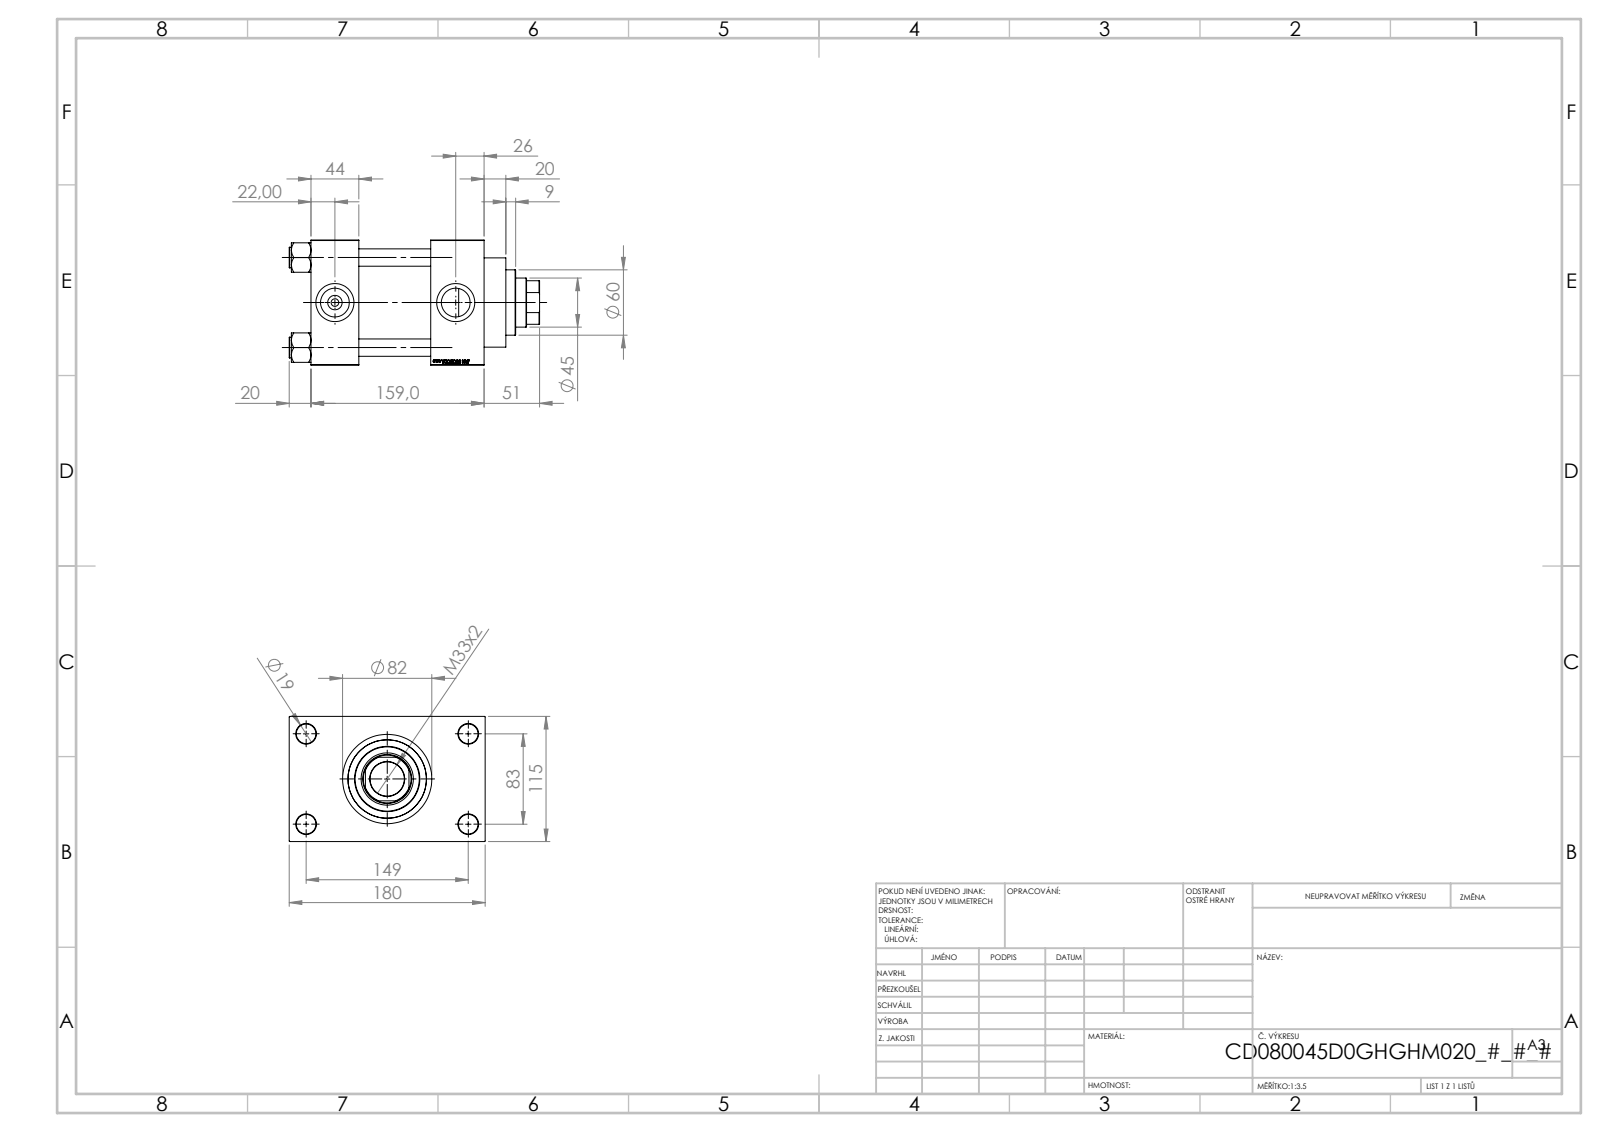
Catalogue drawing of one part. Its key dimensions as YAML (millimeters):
part_name: "V215CD_D_Body; V215CD_VCP_D; V215CD_VC_A; V215CD_NUT_M5_D (+1 more)"
step_written_by: "SolidWorks 2019 (CONFIG_CONTROL_DESIGN)"
units: millimeters
bodies: {solids: 11, faces: 1151, planar: 545, cylindrical: 88, other: 518}
overall_size: [230, 180, 115]
volume: 2004000
surface_area: 302449
round_holes:
  - {diameter: 16, count: 4}
  - {diameter: 18, count: 4}
  - {diameter: 7, count: 2}
  - {diameter: 26.44, count: 2}
  - {diameter: 35, count: 2}
  - {diameter: 31.5, count: 1}
  - {diameter: 45, count: 1}
  - {diameter: 48, count: 1}
  - {diameter: 61, count: 1}
  - {diameter: 72, count: 1}
  - {diameter: 80, count: 1}
round_bosses_or_shafts:
  - {diameter: 19, count: 4}
  - {diameter: 86, count: 1}
  - {diameter: 82, count: 1}
  - {diameter: 60, count: 1}
partial_cylinders:
  - {radius: 22, count: 1}
face_to_face_distances: [115, 110, 66, 49, 44, 159, 32.5, 147.5, 20, 69]
hole_center_spacings: [33.15, 58.48, 82.7, 85.28, 89.24, 115.85, 142.43, 83]
